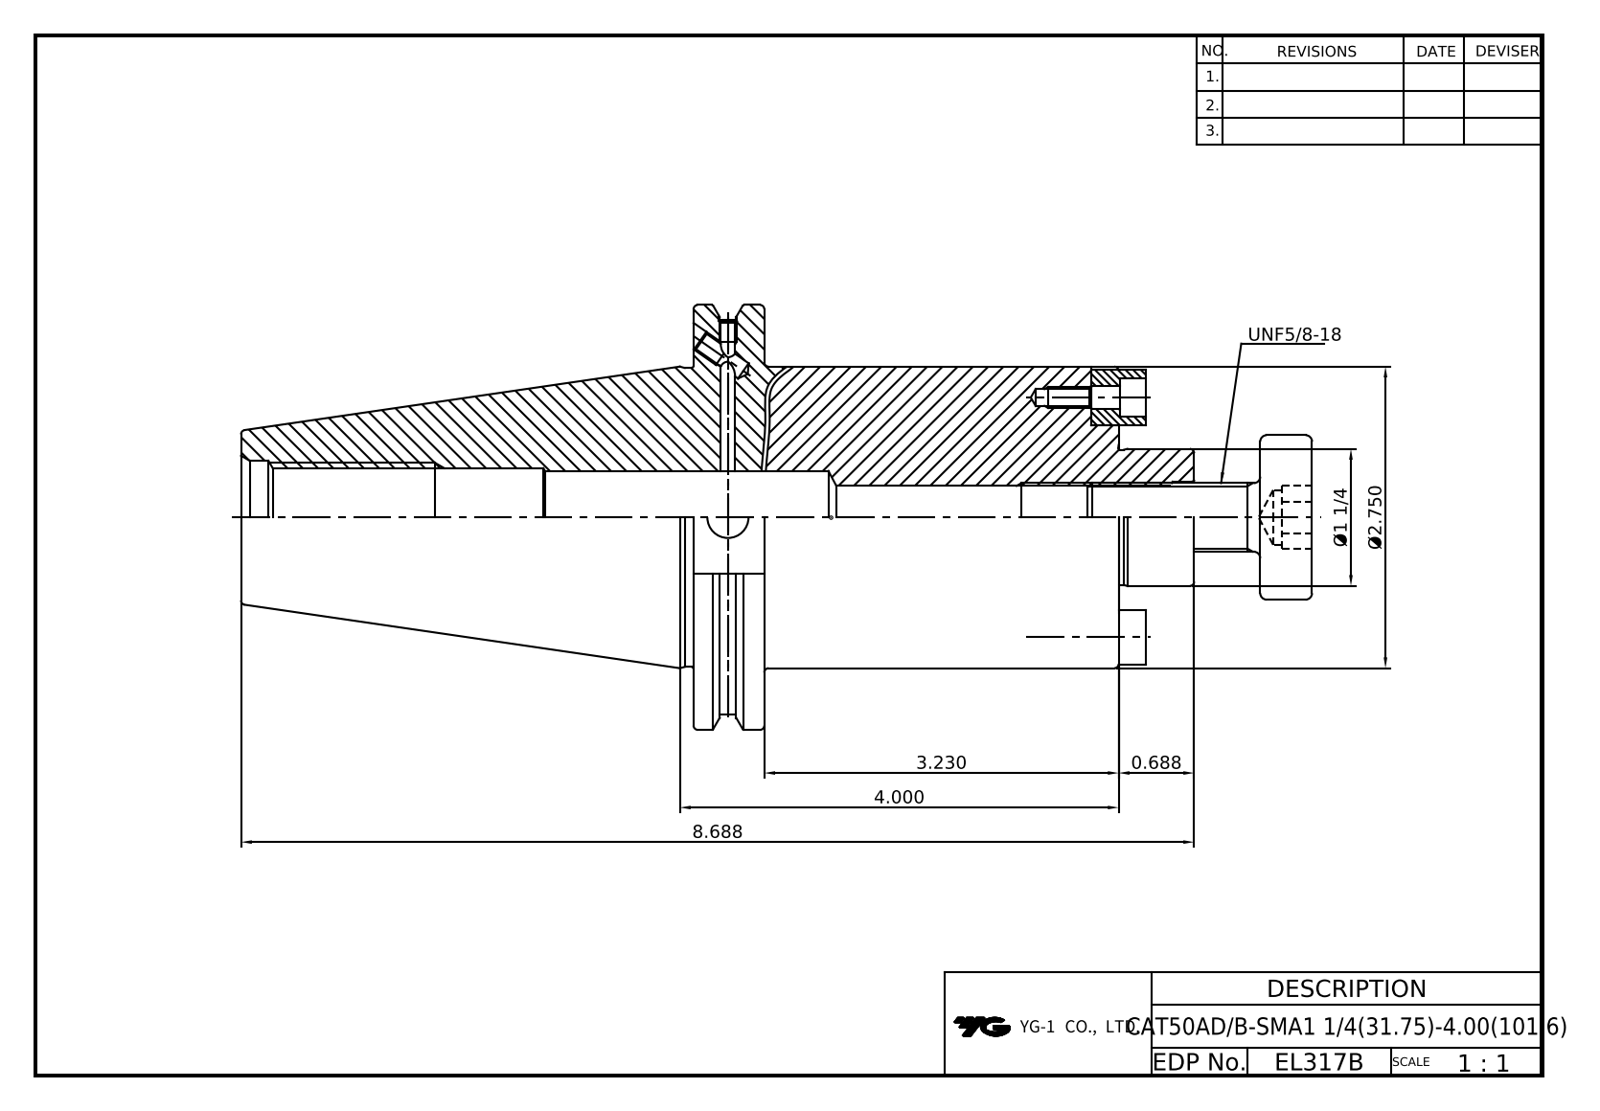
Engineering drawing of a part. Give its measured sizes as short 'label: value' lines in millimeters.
name: LO-CAT50ADB-SMA31.75-101.6; HEX'' WRENCH BOLT-UNC#10-24x1_2L; DRIVE KEY-12.7x12.7x12.7; COLLAR BOLT-UNF5_8-18x40L
written by: Autodesk Inventor 2025 (AP242_MANAGED_MODEL_BASED_3D_ENGINEERING_MIM_LF)
unit: mm
bodies: 6 solids, 163 faces (88 planar, 43 cylindrical, 32 other)
size: 242.7 × 98.4 × 94.7
volume: 649 400 mm³; area: 79 480 mm²
holes: 2× ⌀3.3, 2× ⌀3.7, 2× ⌀4.1, 2× ⌀4.2, 2× ⌀5, 2× ⌀5.5, 2× ⌀8.7, 1× ⌀9.5, 1× ⌀12.7, 1× ⌀14.4, 1× ⌀16.5, 1× ⌀22
bosses: 2× ⌀7.9, 2× ⌀4.8, 1× ⌀98.4, 1× ⌀91.3, 1× ⌀69.9, 1× ⌀69.2, 1× ⌀38.1, 1× ⌀31.8
rounds: 2× R6.4
face distances: 15.9, 98.4, 82.6, 137.9, 122, 39.5, 6.4, 125.9, 110, 27.5
hole spacings: 27.8, 27.8, 55.5, 55.5, 55.5
